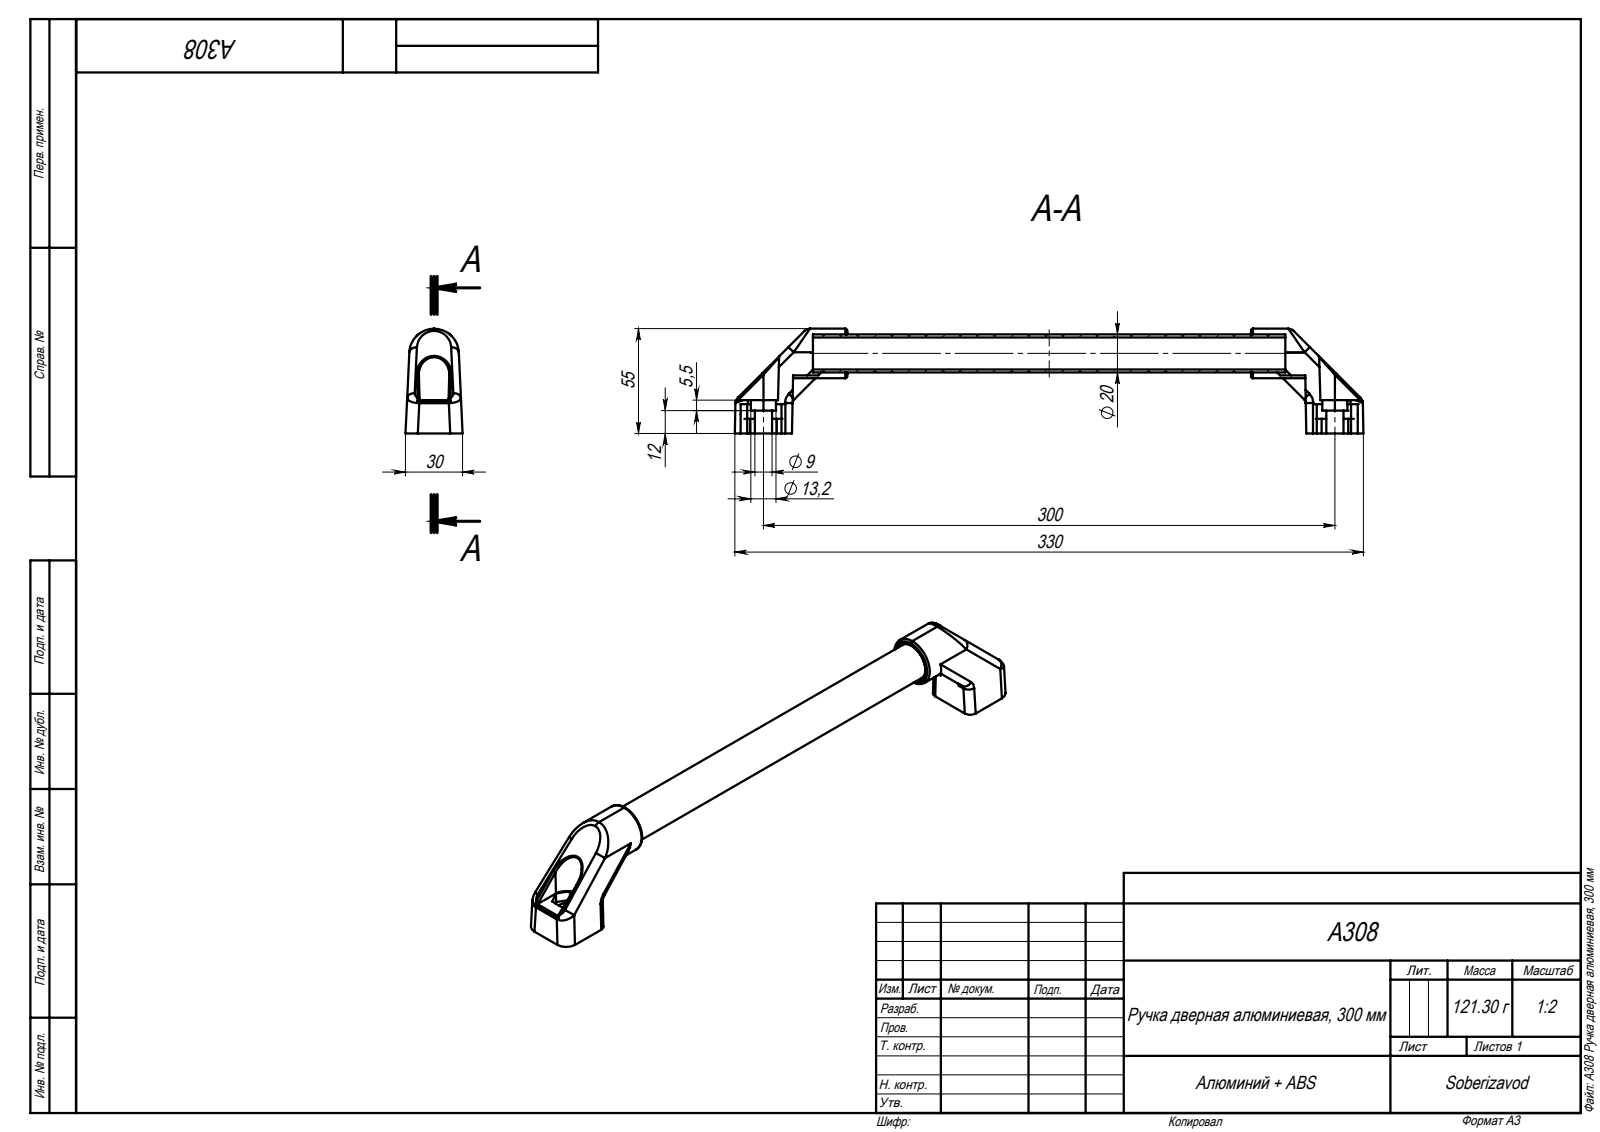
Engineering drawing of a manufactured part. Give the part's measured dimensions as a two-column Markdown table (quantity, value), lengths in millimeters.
| quantity | value |
| --- | --- |
| part name | Основание ручки 250мм_00; Ручка дверная алюминиевая, 300 мм |
| STEP written by | SolidWorks 2018 (AUTOMOTIVE_DESIGN) |
| units | millimeters |
| bodies | 1 solid, 144 faces (60 planar, 48 cylindrical, 36 other) |
| overall size | 330 × 55 × 30 |
| volume | 22 937 mm³ |
| surface area | 49 554 mm² |
| round holes (diameter × count) | 9 × 2, 16.8 × 1 |
| round bosses / shafts (diameter × count) | 14 × 2, 26 × 1, 20 × 1 |
| partial cylindrical surfaces (radius × count) | 4 × 14, 1 × 6, 2 × 4, 3.5 × 4, 3 × 2 |
| main face-to-face distances | 24, 30, 23.5, 300.5, 7.49, 7.7, 277, 17.5, 9.8, 21.56 |
| hole center spacings | 300 |
